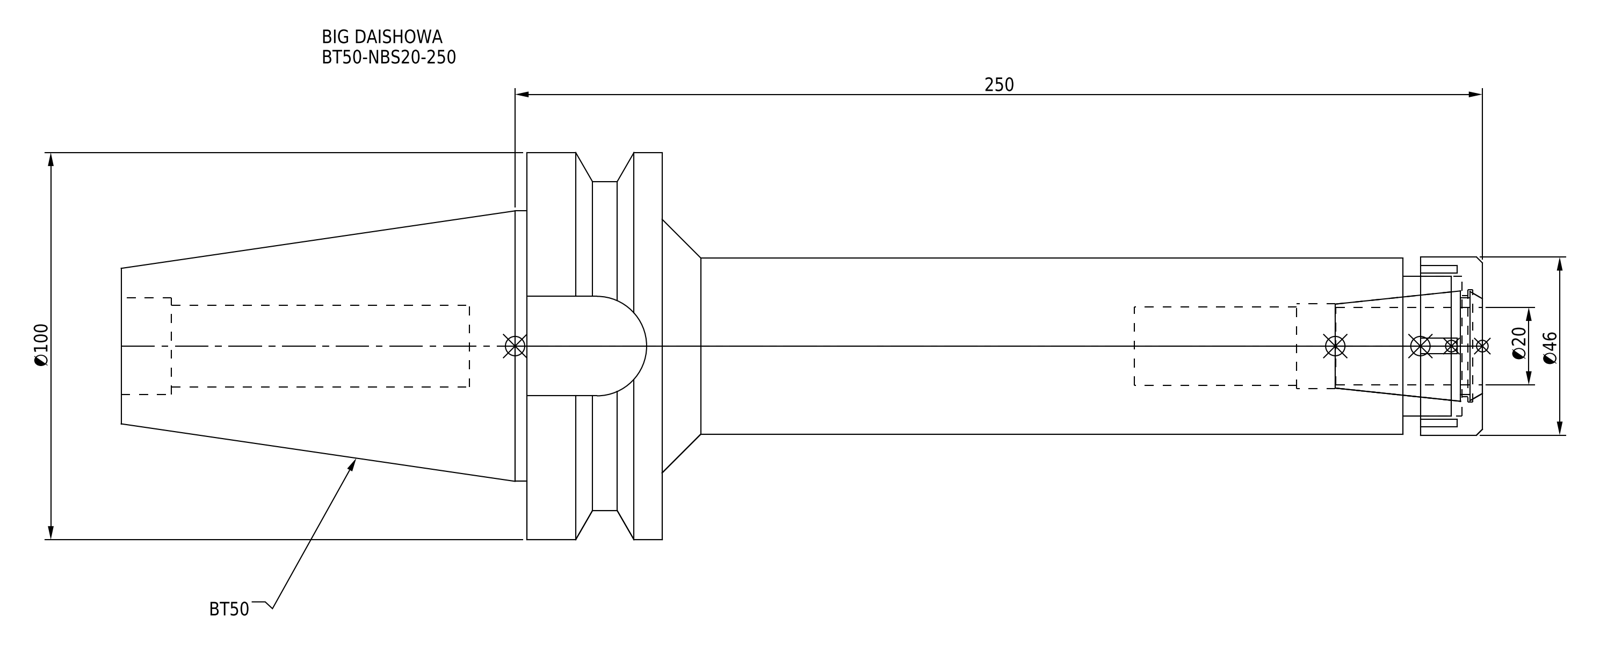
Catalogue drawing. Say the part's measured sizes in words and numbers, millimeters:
The part is named "NBN20_1.stp; DXF_TEMP_ASSY_ASM_4_ASM.stp; BT50NB20250-200_ASM.stp; BT50-NBS20-250_1.stp (+3 more)". Its 3-D file was written by "SolidWorks 2019 (CONFIG_CONTROL_DESIGN)". It is 2 solids with 89 faces: 45 planar, 30 cylindrical and 14 other. Overall it measures 351.8 by 100 by 100 millimeters. Its volume is 772 592 cubic millimeters and its surface area 91 590 square millimeters. Round holes: 1 of diameter 20.3, 1 of diameter 21.2, 1 of diameter 22, 1 of diameter 25, 1 of diameter 26, 1 of diameter 29, 1 of diameter 36. Round bosses or shafts: 1 of diameter 100, 1 of diameter 85, 1 of diameter 69.85, 1 of diameter 46, 1 of diameter 45.5. Partial cylindrical surfaces (rounded edges, fillets, slot ends): 1 of radius 12.85. The main face-to-face distances are 35, 212, 247, 8, 351.8, 139.8, 104.8, 70.8, 90, 261.8.
